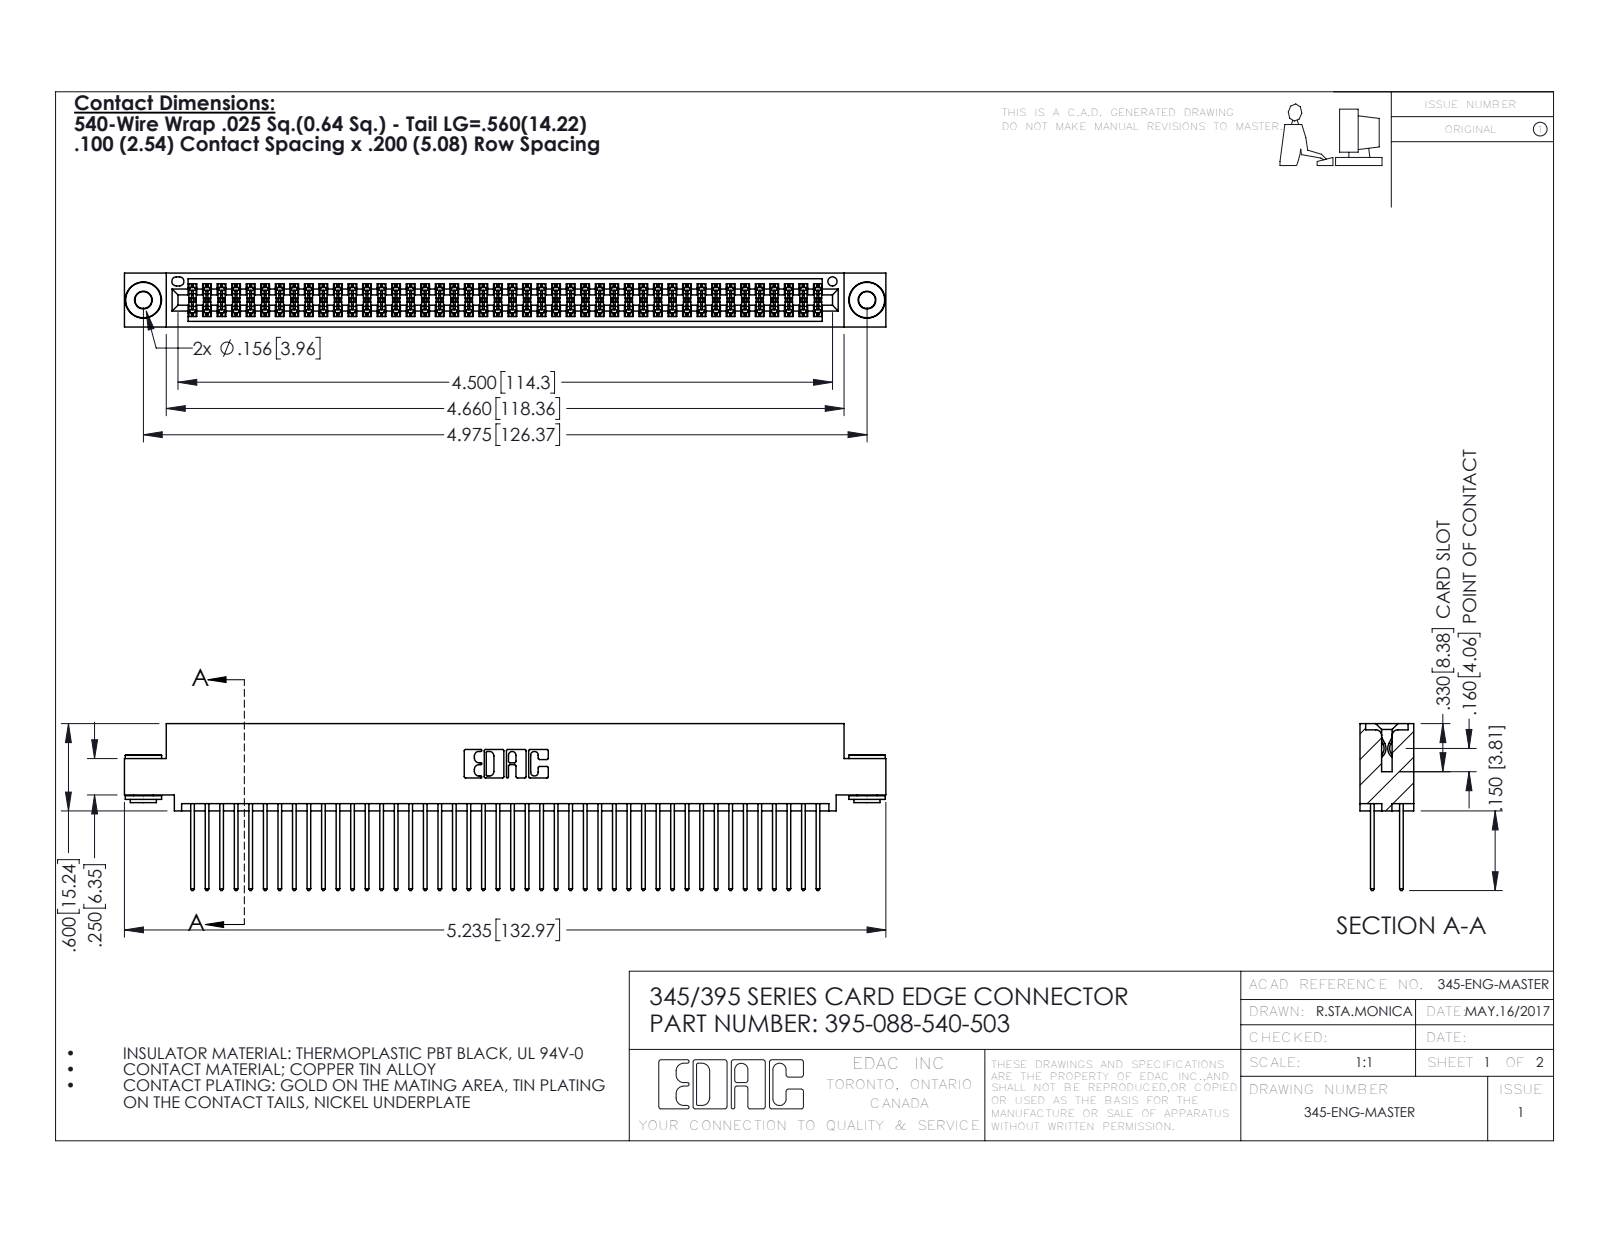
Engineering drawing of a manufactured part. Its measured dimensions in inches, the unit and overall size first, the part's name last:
Units: inches
Overall size (bounding box): 5.235 × 1.147 × 0.37
Round holes (diameter × count): ⌀0.116 ×2, ⌀0.156 ×2, ⌀0.064 ×1
Round bosses / shafts (diameter × count): ⌀0.25 ×2, ⌀0.18 ×2, ⌀0.136 ×2
Partial cylindrical surfaces — rounded edges, fillets, slot ends (radius × count): R0.006 ×132, R0.01 ×88, R0.01 ×22, R0.007 ×6, R0.031 ×6, R0.026 ×3, R0.014 ×2, R0.019 ×2
Main face-to-face distances: 0.072, 0.298, 0.2, 0.025, 0.098, 0.272, 0.37, 0.225, 0.175, 0.149
Hole centre spacings: 0.27, 4.739, 4.975
Volume: 0.806 in³ · Surface area: 33.2 in²
Bodies: 91 solids, 4568 faces (2998 planar, 1562 cylindrical, 8 other)
Part name (STEP PRODUCT): 345-250-002_345-250-002-102; 395-088-540-503; 345-292-001_345-293-140; 345 Part_0.110 Offset - 0.156 Dia-TH
STEP written by: SolidWorks 2016 (CONFIG_CONTROL_DESIGN)
